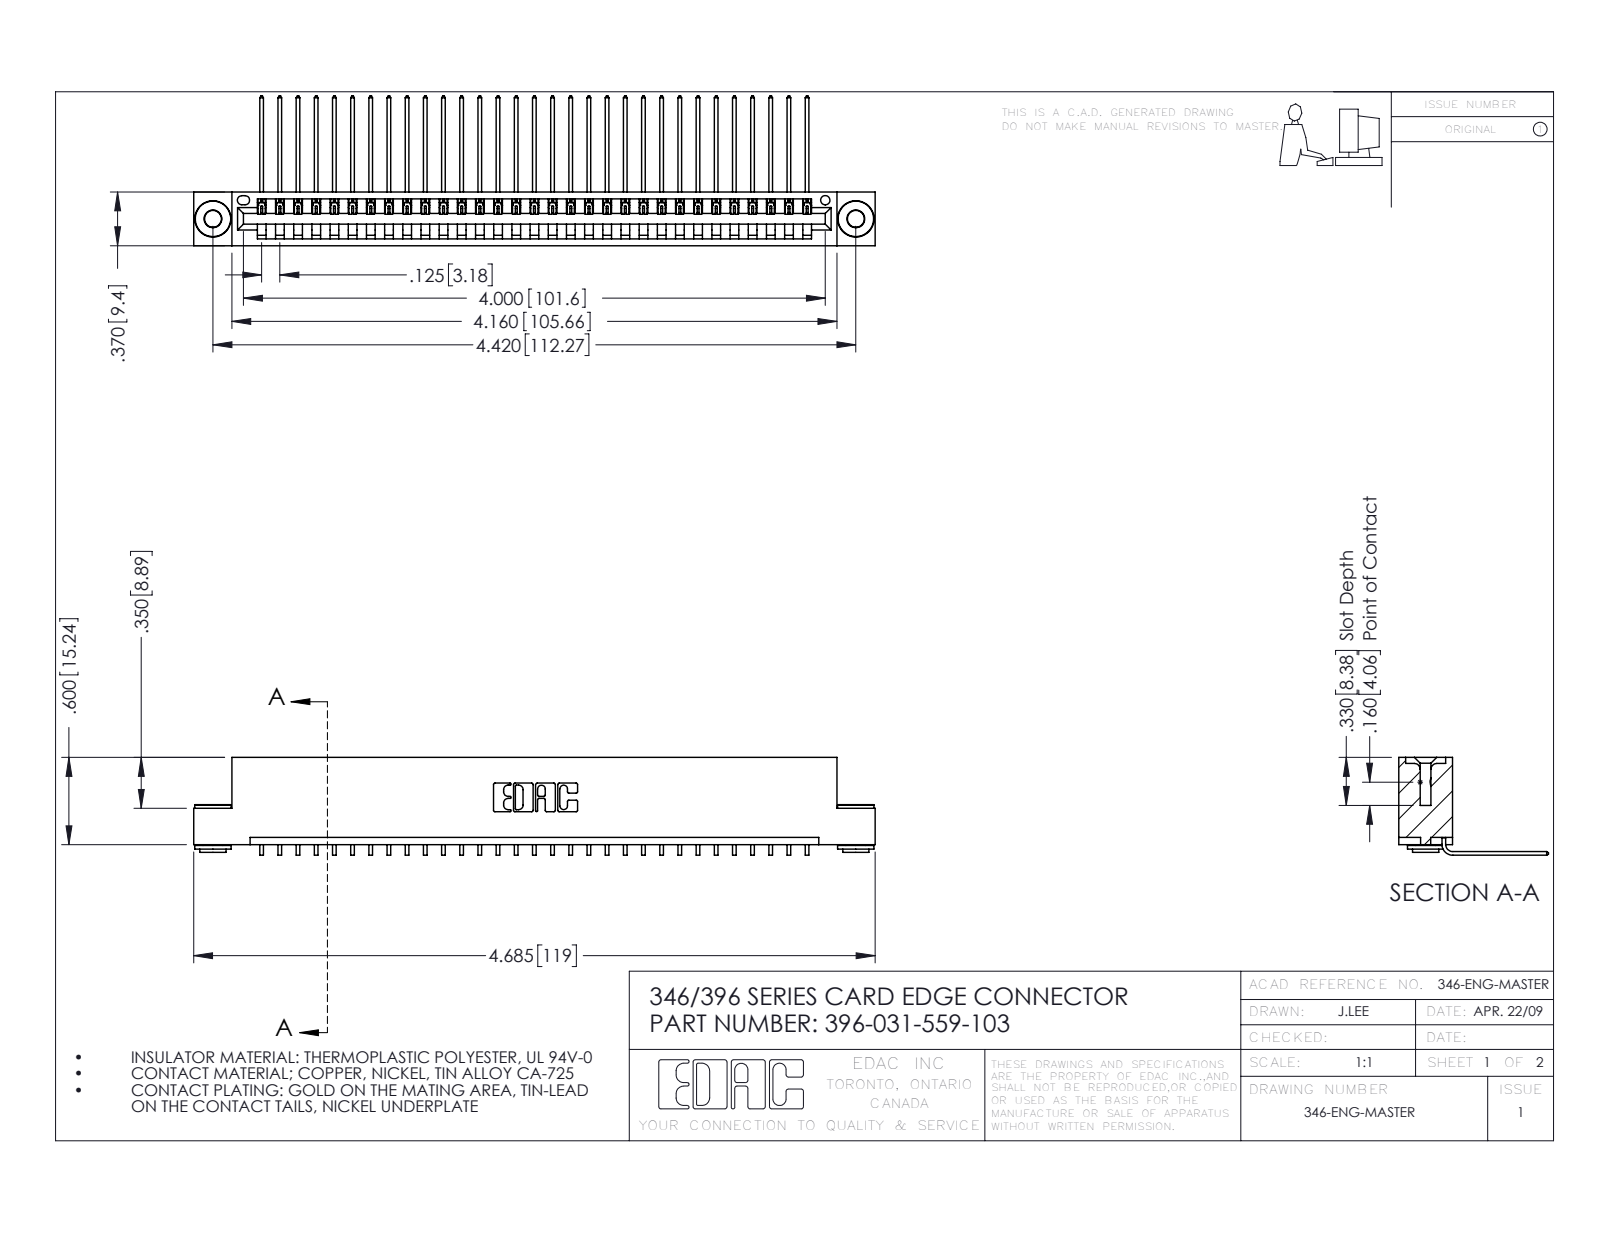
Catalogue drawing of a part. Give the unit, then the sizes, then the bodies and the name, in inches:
Units: inches
Overall size (bounding box): 4.685 × 1.03 × 0.673
Round holes (diameter × count): ⌀0.116 ×2, ⌀0.156 ×2, ⌀0.064 ×1
Round bosses / shafts (diameter × count): ⌀0.25 ×2, ⌀0.18 ×2, ⌀0.136 ×2
Partial cylindrical surfaces — rounded edges, fillets, slot ends (radius × count): R0.006 ×62, R0.01 ×22, R0.007 ×6, R0.031 ×6, R0.026 ×3, R0.031 ×2, R0.04 ×2, R0.014 ×1
Main face-to-face distances: 0.048, 0.322, 0.37, 0.25, 0.025, 0.072, 0.298, 0.148, 0.222, 0.1
Hole centre spacings: 0.246, 4.212, 4.42
Volume: 0.698 in³ · Surface area: 23.27 in²
Bodies: 34 solids, 2020 faces (1388 planar, 624 cylindrical, 8 other)
Part name (STEP PRODUCT): 345-250-002_345-250-002-102; 345-292-001_558 559 Tail - 1; 346 Part_Flush Mounting Lugs - 0.156 Dia-TH; 396-031-559-103
STEP written by: SolidWorks 2016 (CONFIG_CONTROL_DESIGN)
